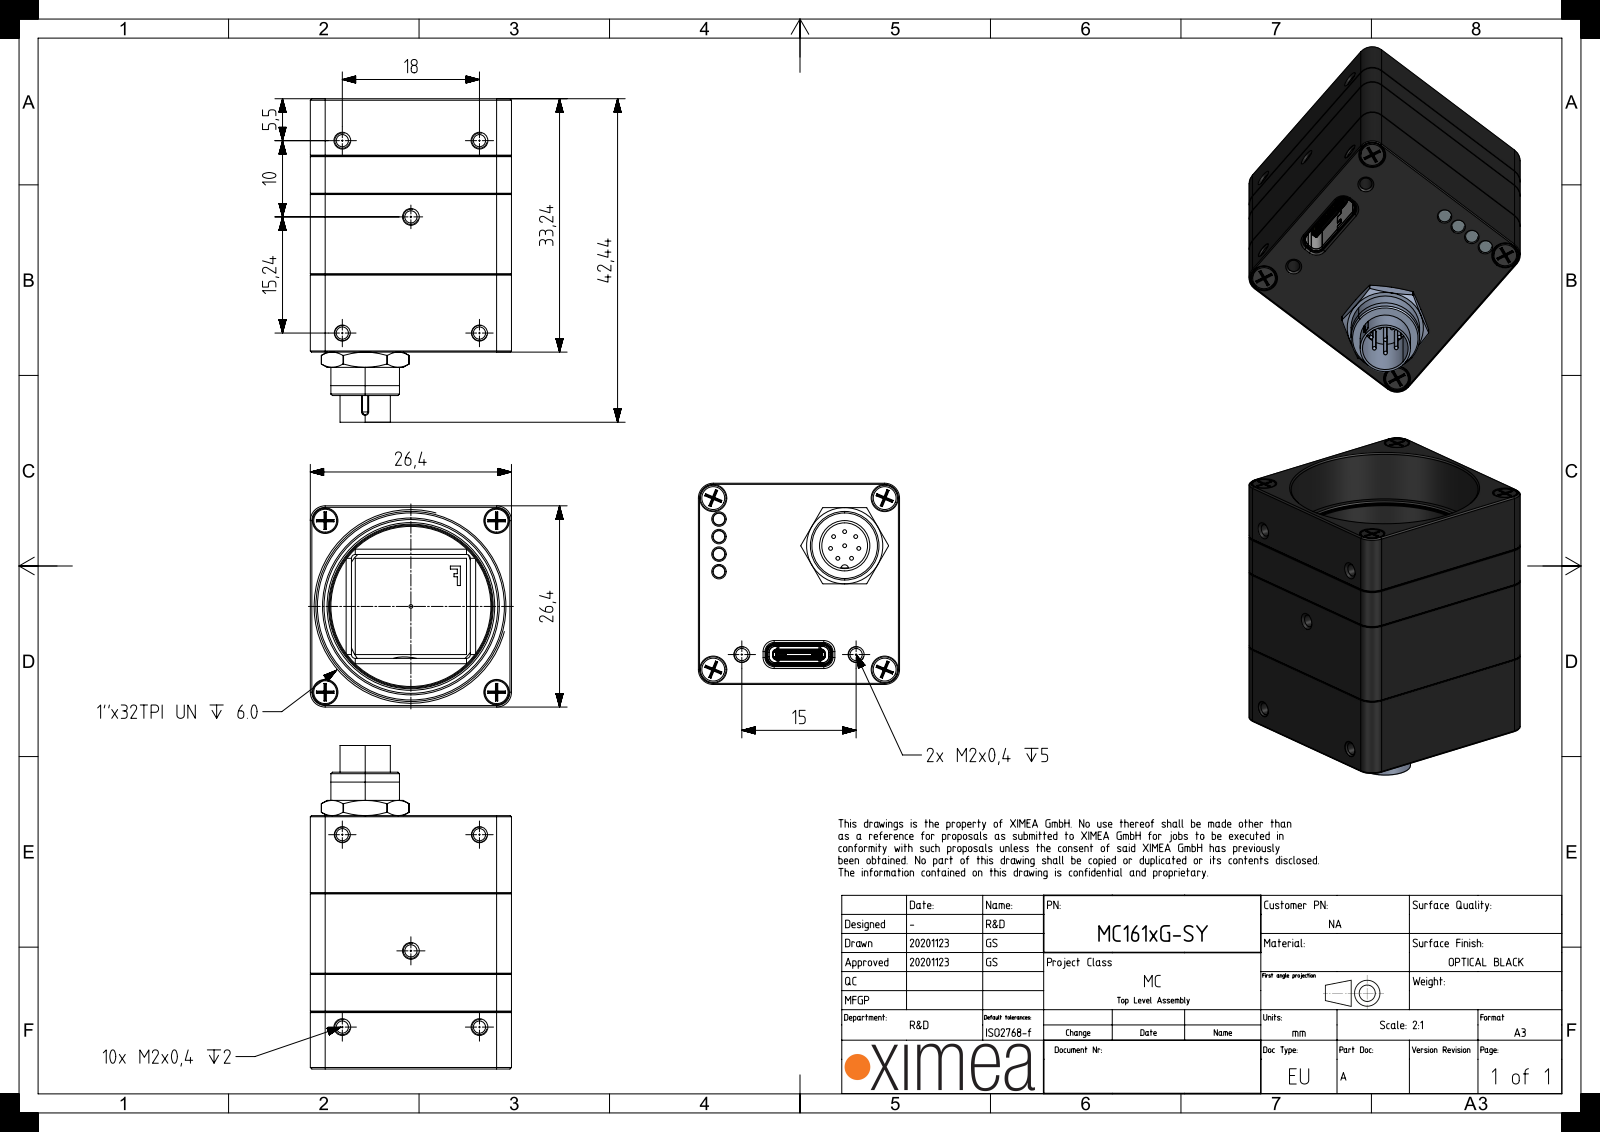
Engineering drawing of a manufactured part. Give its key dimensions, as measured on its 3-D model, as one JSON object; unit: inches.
{"part_name": "MT160xG-PR-SENSOR-PCA-LW; MECH-CB262-ANTIDUST-GSKT; MECH-O-RING-22X1-VI370; FLT-BK7-AR2X-D25 (+8 more)", "step_written_by": "SIEMENS PLM Software NX 1907 (AUTOMOTIVE_DESIGN)", "units": "inches", "bodies": {"solids": 36, "faces": 7452, "planar": 5275, "cylindrical": 1827, "other": 350}, "overall_size": [1.671, 1.039, 1.039], "volume_in3": 0.735, "surface_area_in2": 31.84, "round_holes": [[0.063, 15], [0.031, 8], [0.035, 4], [0.079, 4], [0.083, 4], [0.118, 4], [0.126, 4], [0.132, 4], [0.028, 2], [0.051, 2], [0.067, 2], [0.026, 1]], "round_bosses_or_shafts": [[0.024, 8], [0.02, 8], [0.075, 4], [0.064, 4], [0.033, 4], [0.118, 2], [0.063, 2], [0.025, 2]], "partial_cylinders_radius": [[0.004, 54], [0.006, 51], [0.008, 28], [0.01, 18], [0.015, 18], [0.013, 16], [0.039, 14], [0.059, 14]], "face_to_face_distances": [1.039, 0.039, 0.142, 0.458, 0.317, 0.102, 0.419, 0.524, 0.04, 0.277], "hole_center_spacings": [0.074, 0.626, 0.886, 0.091, 0.114, 0.148, 0.181, 0.738]}
